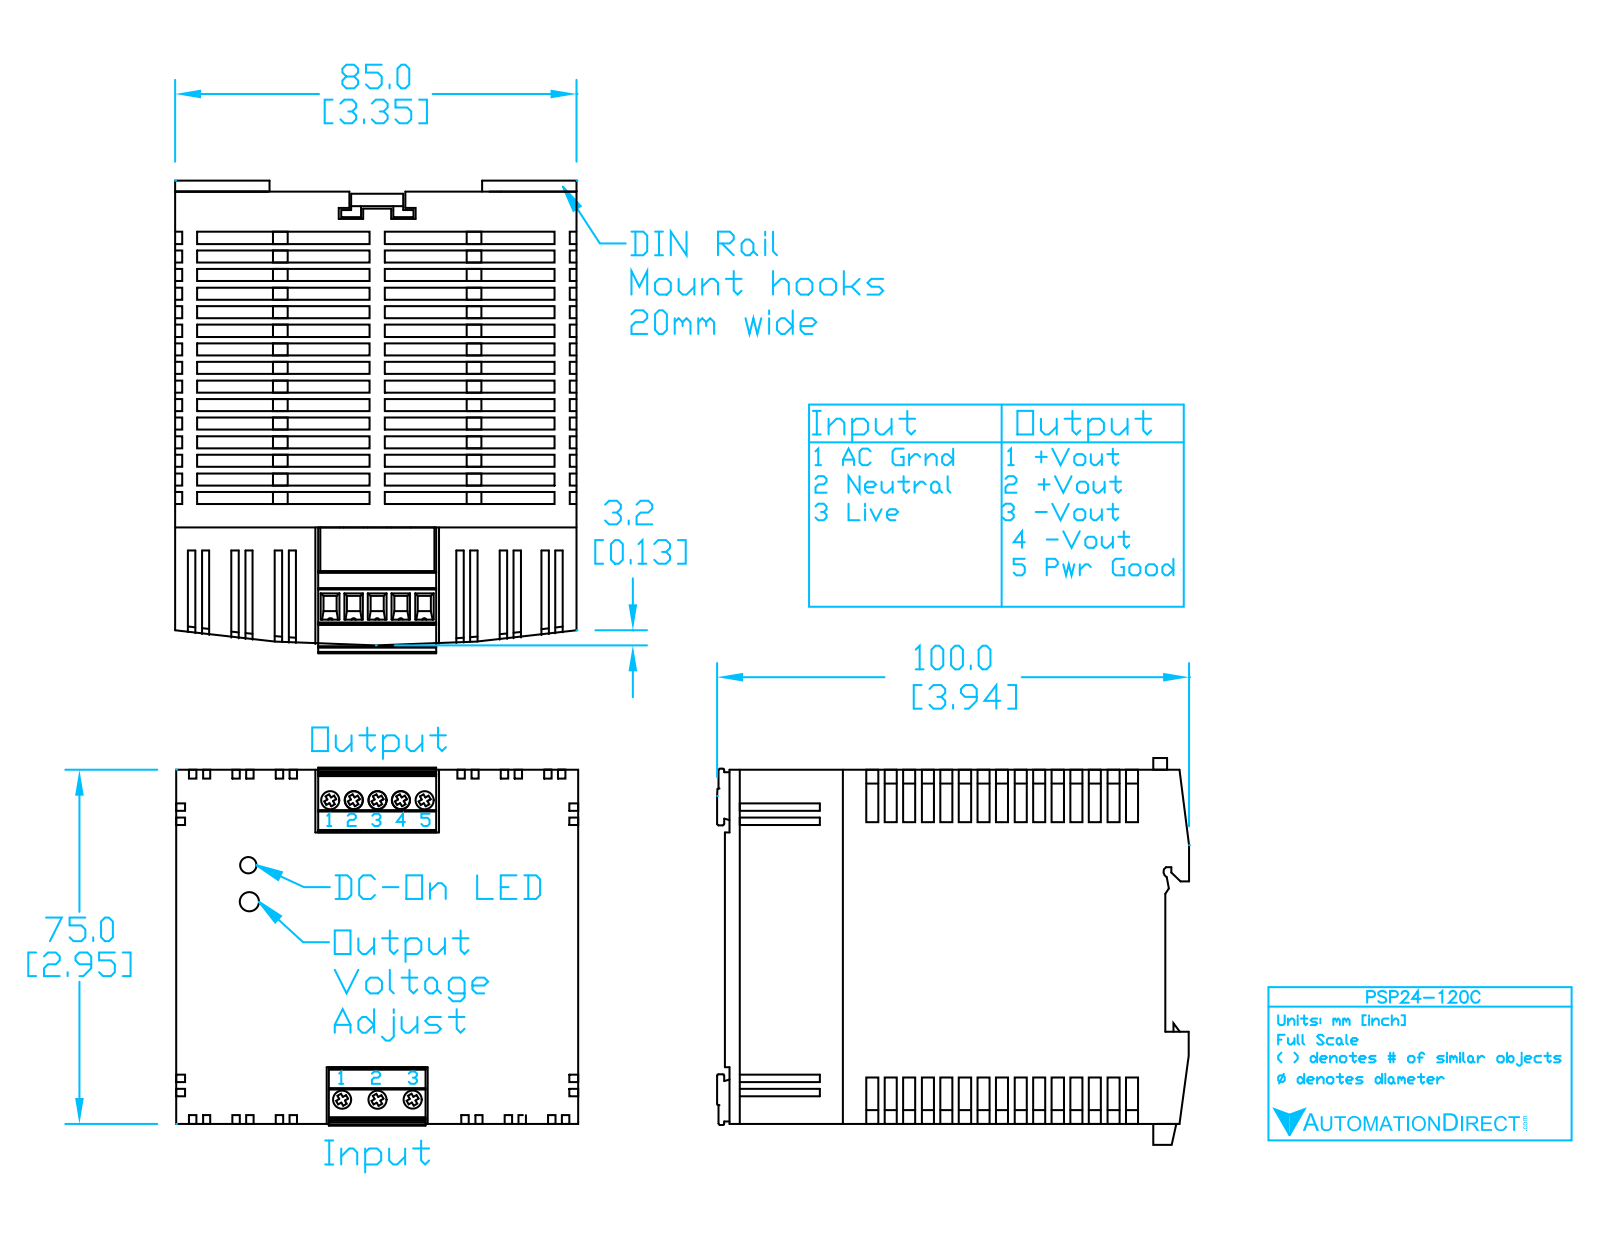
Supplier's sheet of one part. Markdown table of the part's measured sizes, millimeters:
| quantity | value |
| --- | --- |
| part name | PSP24-120C |
| STEP written by | SolidWorks 2011 (CONFIG_CONTROL_DESIGN) |
| units | millimeters |
| bodies | 4 solids, 488 faces (417 planar, 0 cylindrical, 71 other) |
| overall size | 100.5 × 85 × 80 |
| volume | 701 409 mm³ |
| surface area | 71 783 mm² |
| main face-to-face distances | 75, 85, 68.85, 68.95, 14.16, 60.84, 59.67, 45.51, 15.33, 2.48 |
